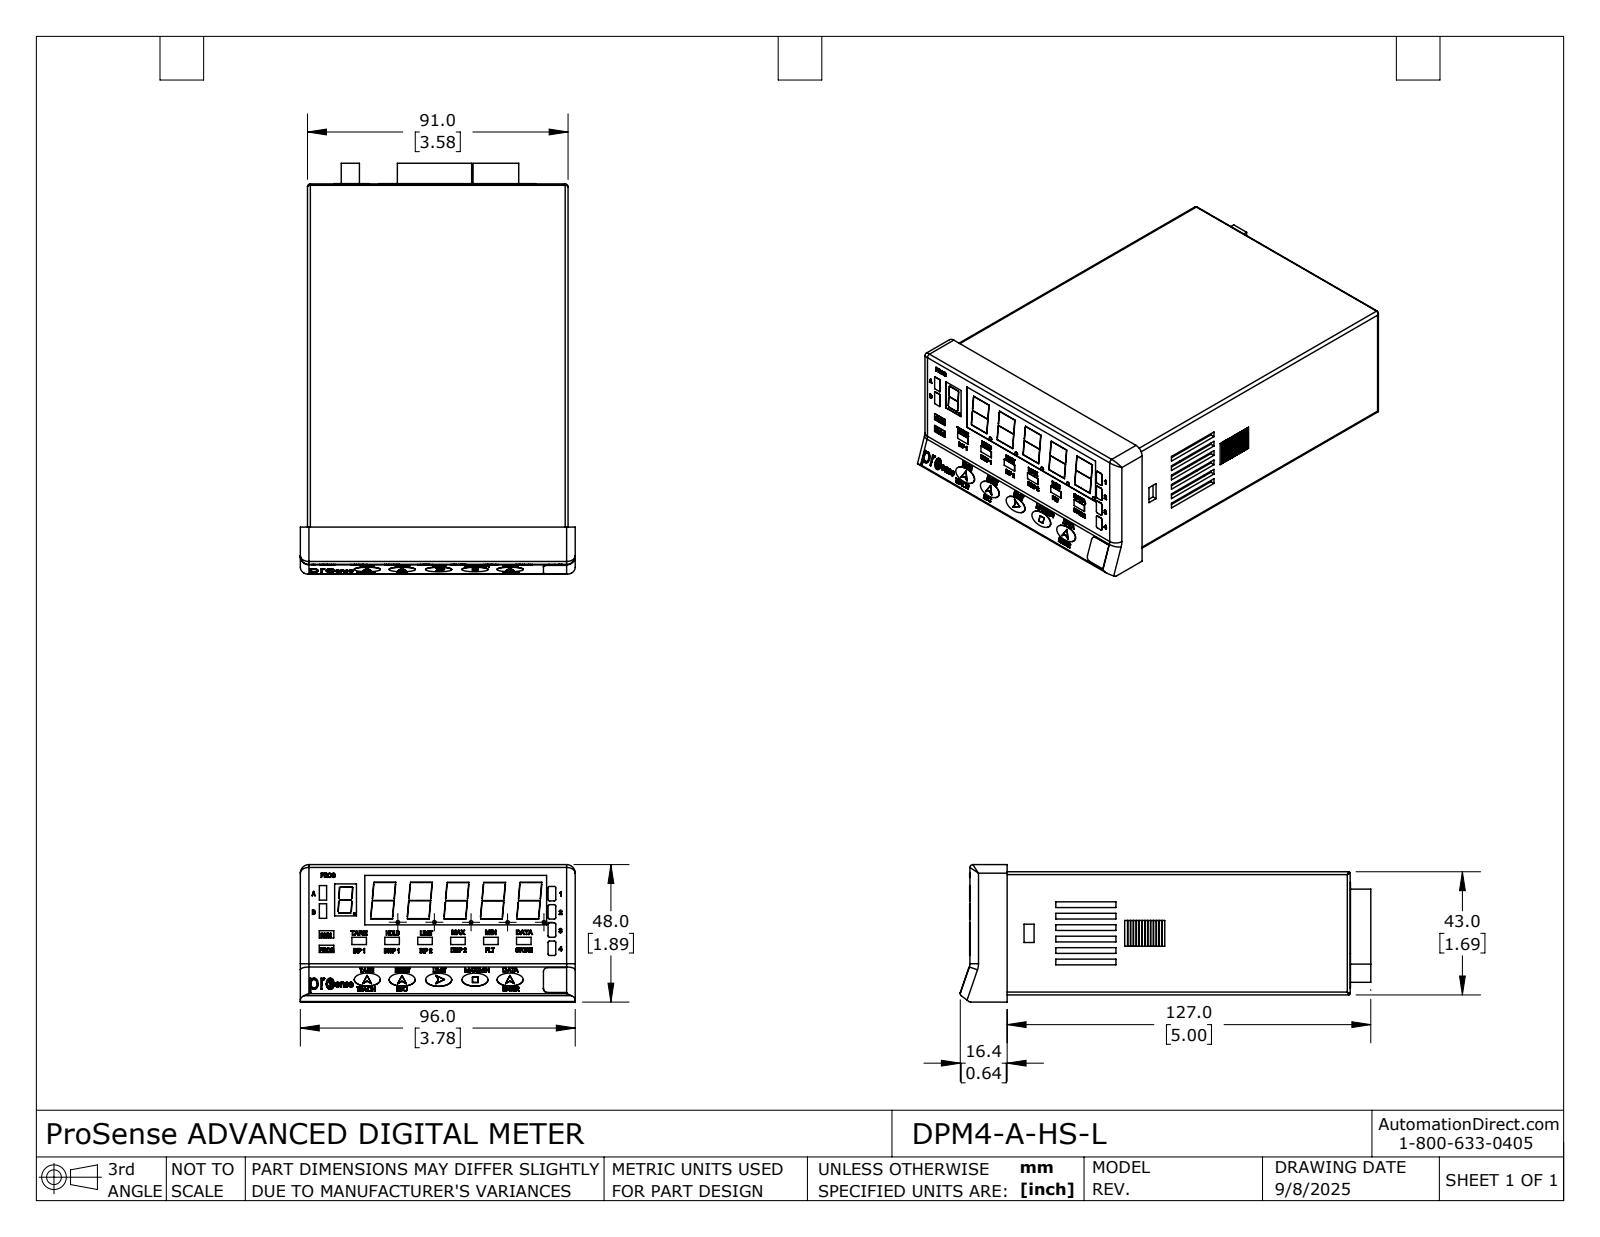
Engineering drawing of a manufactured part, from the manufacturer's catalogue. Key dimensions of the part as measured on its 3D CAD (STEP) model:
Part name (STEP PRODUCT): DPM4-A-HS-L
STEP written by: SolidWorks 2024 (AUTOMOTIVE_DESIGN)
Units: inches
Bodies: 6 solids, 2326 faces (1804 planar, 77 cylindrical, 445 other)
Overall size (bounding box): 5.647 × 3.78 × 1.89
Volume: 18.99 in³ · Surface area: 112.3 in²
Round bosses / shafts (diameter × count): ⌀0.078 ×14, ⌀0.047 ×5
Partial cylindrical surfaces — rounded edges, fillets, slot ends (radius × count): R0.02 ×18, R0.039 ×8, R0.118 ×6, R0.004 ×2, R0.059 ×2, R0.03 ×1, R0.138 ×1, R0.197 ×1
Main face-to-face distances: 0.059, 1.693, 1.634, 0.098, 3.583, 1.575, 1.732, 3.524, 0.157, 2.823
